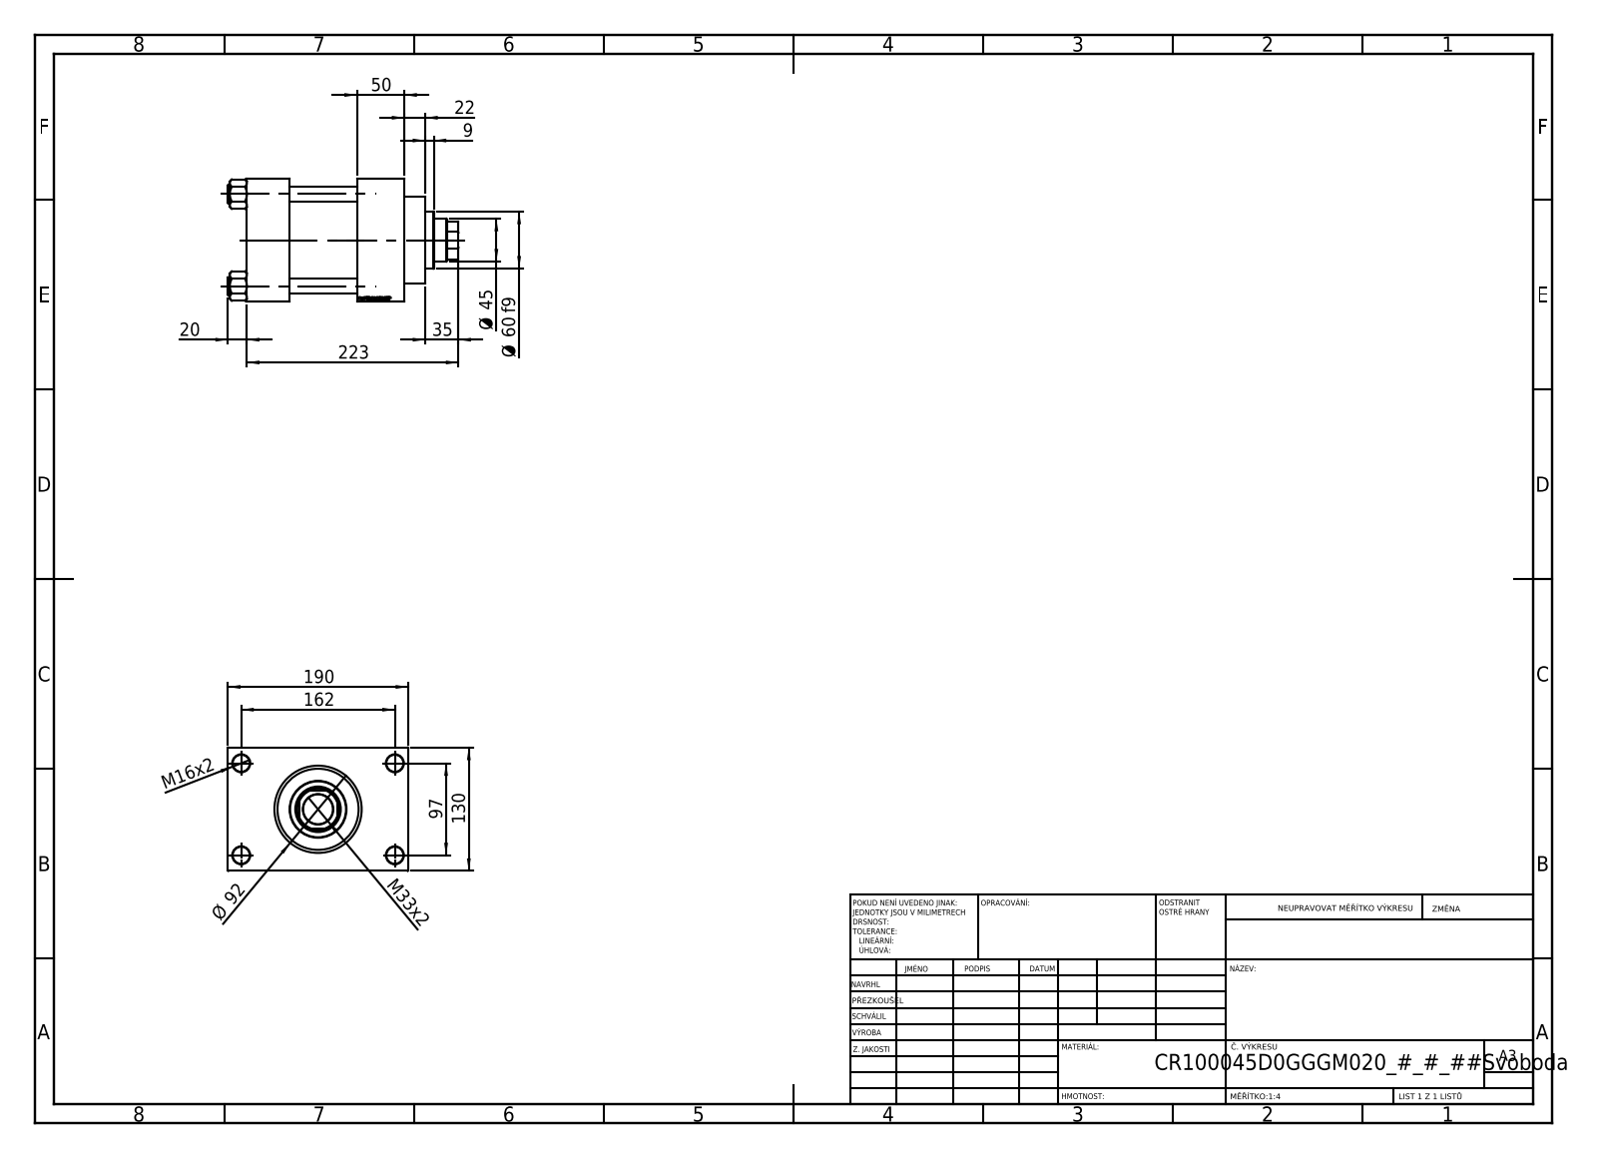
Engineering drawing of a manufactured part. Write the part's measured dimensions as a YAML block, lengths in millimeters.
part_name: "V215_VC_A; NUT_M5_D; V215CR_D_Body; V215CR_D_TYCINKA (+1 more)"
step_written_by: "SolidWorks 2019 (CONFIG_CONTROL_DESIGN)"
units: millimeters
bodies: {solids: 11, faces: 1152, planar: 545, cylindrical: 89, other: 518}
overall_size: [243, 190, 130]
volume: 2607000
surface_area: 352394
round_holes:
  - {diameter: 16, count: 4}
  - {diameter: 18, count: 4}
  - {diameter: 7, count: 2}
  - {diameter: 26.44, count: 2}
  - {diameter: 35, count: 2}
  - {diameter: 31.5, count: 1}
  - {diameter: 45, count: 1}
  - {diameter: 48, count: 1}
  - {diameter: 76, count: 1}
  - {diameter: 85.5, count: 1}
  - {diameter: 100, count: 1}
round_bosses_or_shafts:
  - {diameter: 19, count: 4}
  - {diameter: 106, count: 1}
  - {diameter: 92, count: 1}
  - {diameter: 60, count: 1}
partial_cylinders:
  - {radius: 22, count: 1}
face_to_face_distances: [130, 45, 116, 71, 166, 121, 50, 30, 160, 20]
hole_center_spacings: [32.55, 68.52, 94.41, 96.9, 102.27, 129.45, 161.73, 97]
